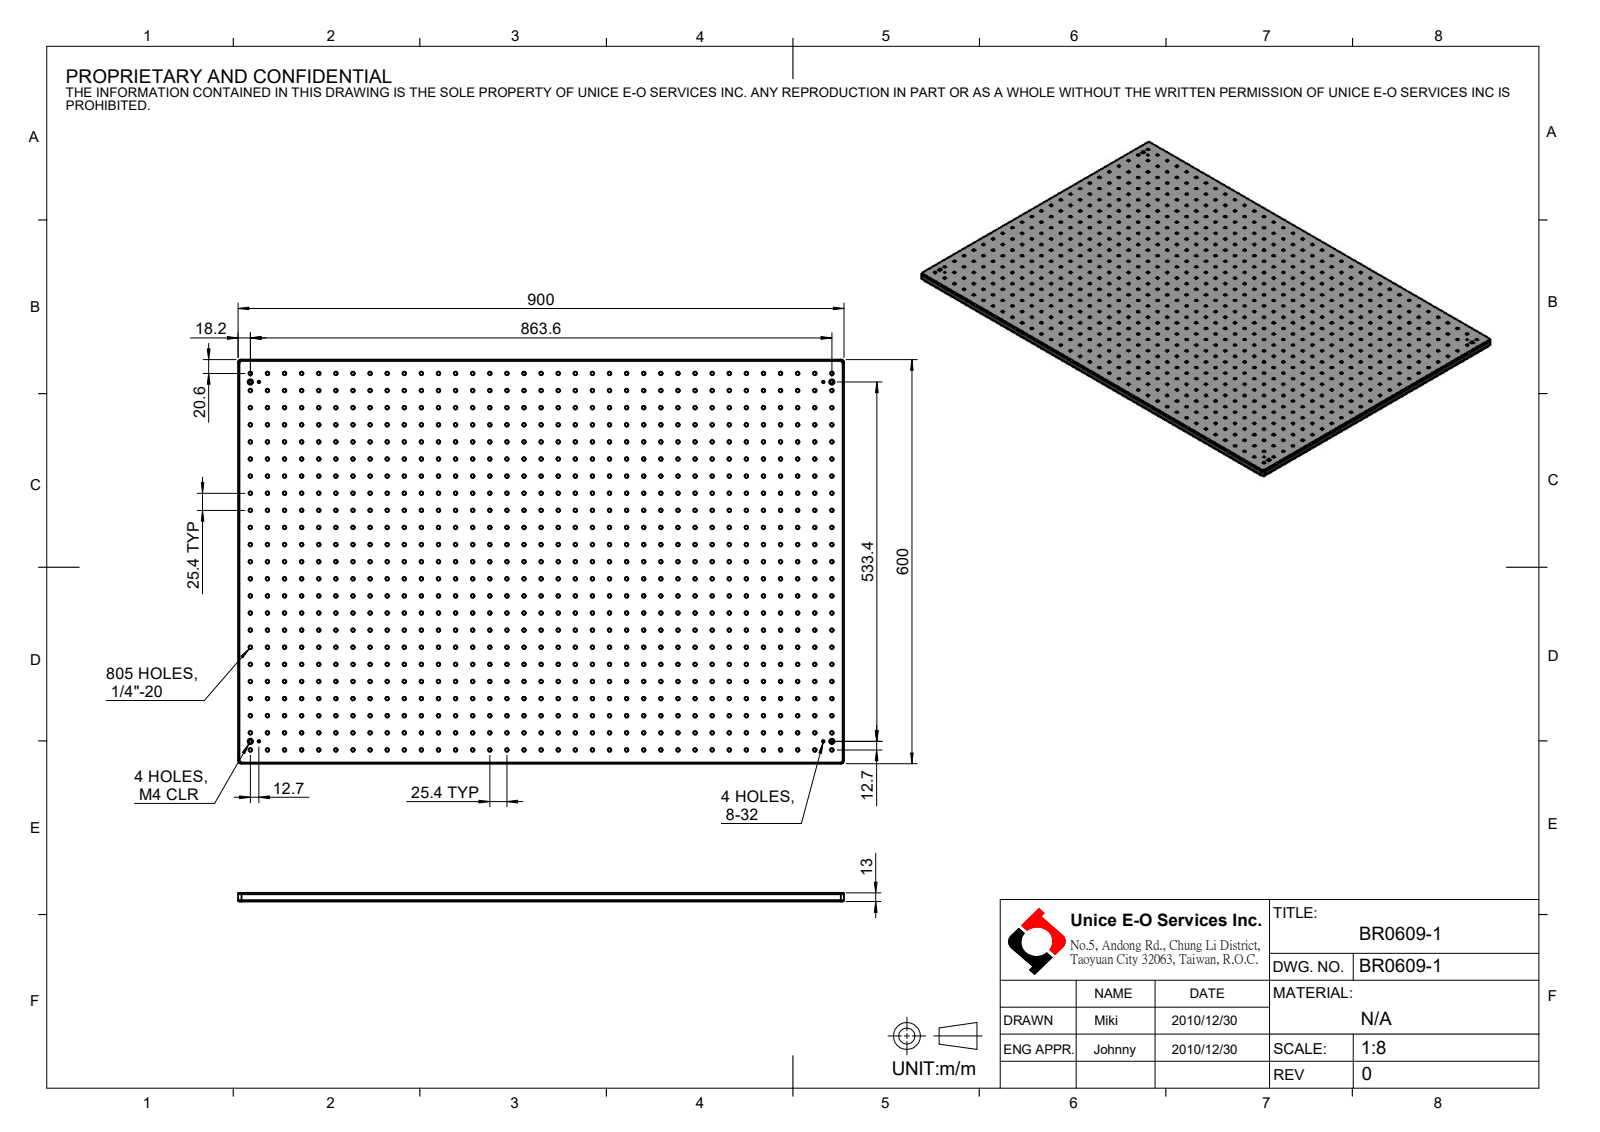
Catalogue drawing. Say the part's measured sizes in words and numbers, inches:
The part is named "BR0609-1". Its 3-D file was written by "SolidWorks 2016 (CONFIG_CONTROL_DESIGN)". It is 1 solid with 1664 faces: 10 planar, 1646 cylindrical and 8 other. Overall it measures 35.433 by 23.622 by 0.512 inches. Its volume is 414.8 cubic inches and its surface area 1 938 square inches. Round holes: 805 of diameter 0.201, 4 of diameter 0.136, 4 of diameter 0.177, 4 of diameter 0.315. Partial cylindrical surfaces (rounded edges, fillets, slot ends): 8 of radius 0.079, 4 of radius 0.197. The main face-to-face distances are 0.512, 23.622, 35.433, 0.276, 0.236. The hole center spacings are 1, 2, 3, 4, 5, 6, 7, 8.
